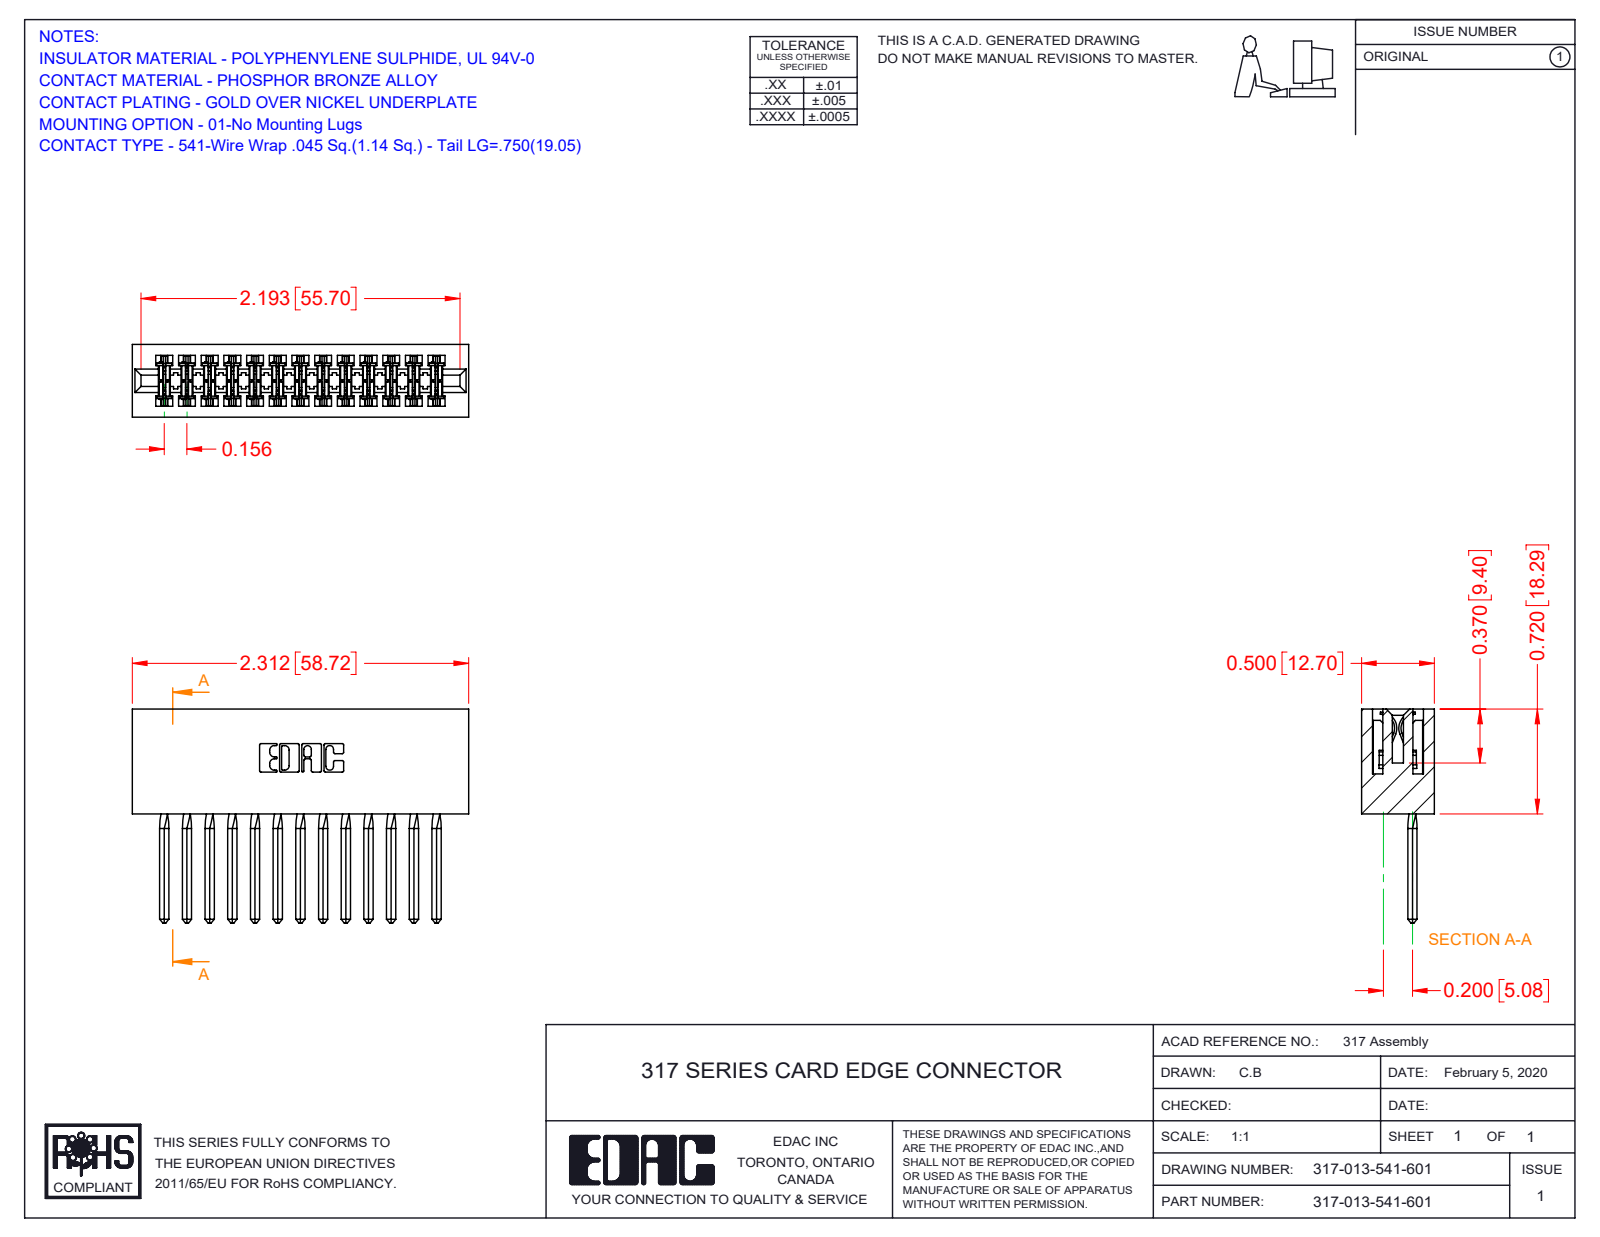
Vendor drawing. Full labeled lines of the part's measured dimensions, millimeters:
Part name (STEP PRODUCT): 317 Part_Lugless; 317-013-541-601; 317-290-002_541
STEP written by: SolidWorks 2016 (CONFIG_CONTROL_DESIGN)
Units: millimetres
Bodies: 14 solids, 2066 faces (1662 planar, 352 cylindrical, 52 other)
Overall size (bounding box): 58.7 × 37.3 × 12.7
Volume: 10 300 mm³ · Surface area: 13 830 mm²
Partial cylindrical surfaces — rounded edges, fillets, slot ends (radius × count): R0.4 ×26, R0.3 ×22, R0.2 ×6, R0.8 ×6, R0.7 ×3, R2.4 ×2, R2.5 ×2, R2.8 ×2
Main face-to-face distances: 12.7, 1.9, 10.8, 2.8, 5.6, 1.7, 8.9, 4, 8.4, 5
